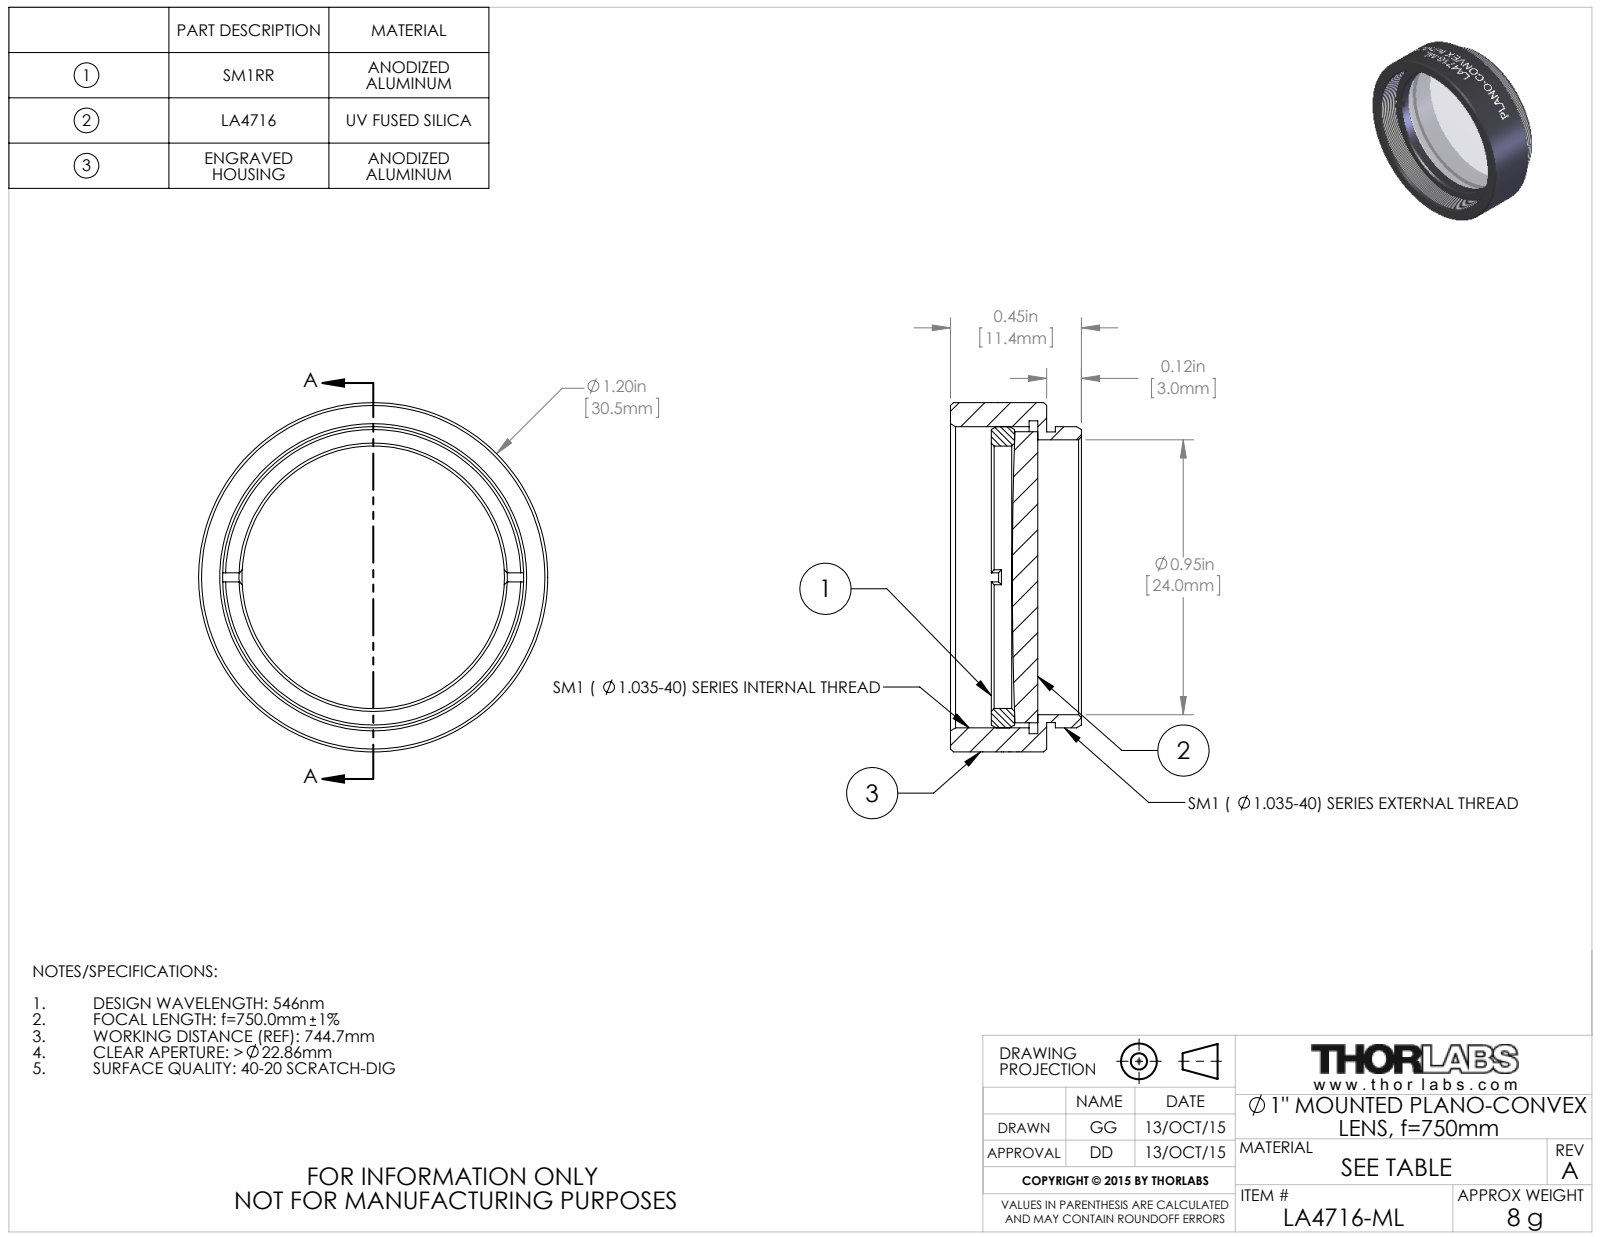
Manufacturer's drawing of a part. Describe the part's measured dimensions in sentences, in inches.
The part is named "TTN039354-E0W". Its 3-D file was written by "SolidWorks 2014 (CONFIG_CONTROL_DESIGN)". It is 3 solids with 121 faces: 20 planar, 77 cylindrical and 24 other. Overall it measures 1.2 by 1.2 by 0.45 inches. Its volume is 0.192 cubic inches and its surface area 6.685 square inches. Round holes: 1 of diameter 0.902, 1 of diameter 0.945, 1 of diameter 1.075. Round bosses or shafts: 1 of diameter 1.2, 1 of diameter 1.035, 1 of diameter 1, 1 of diameter 0.999. The main face-to-face distances are 0.03, 0.33, 0.3, 0.11, 0.08, 0.22, 0.19, 0.16, 0.08, 0.14.
